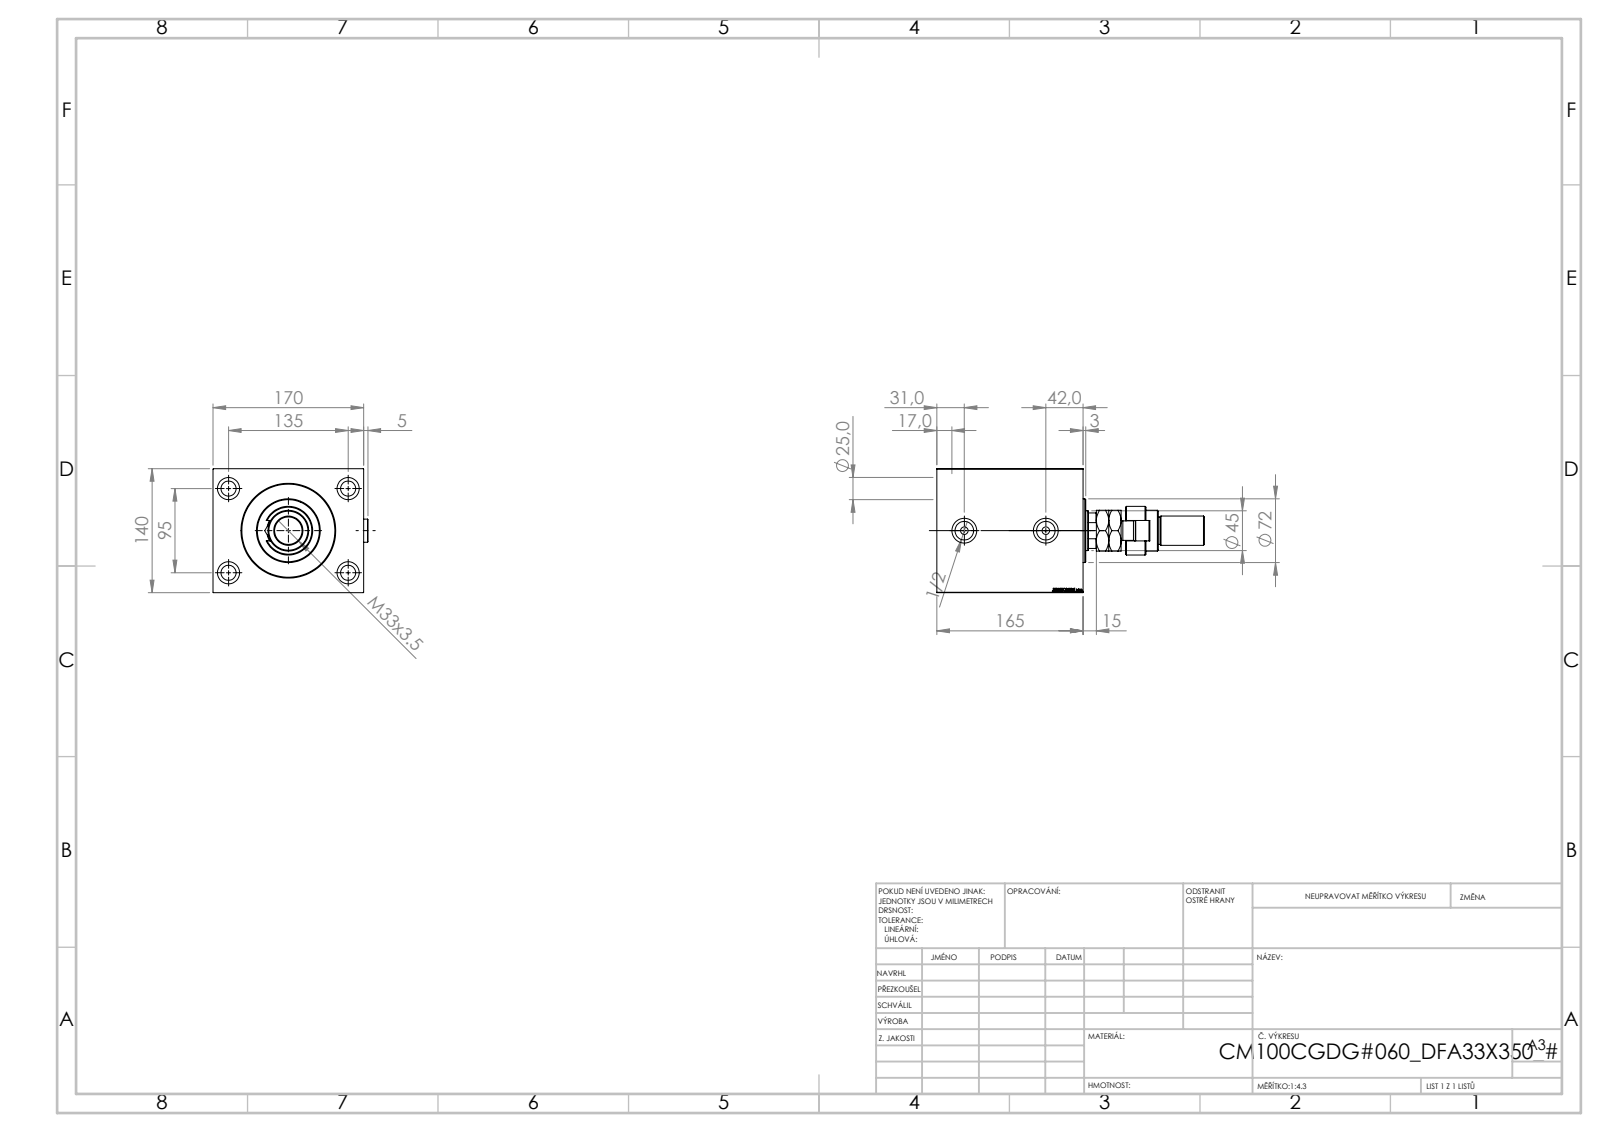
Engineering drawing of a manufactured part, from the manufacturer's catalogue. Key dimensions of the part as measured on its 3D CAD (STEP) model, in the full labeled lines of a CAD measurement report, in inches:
Part name (STEP PRODUCT): V450CM_VC_B; V450CM_C_Body; FEMALE_PART_FOR_DFA; V450CM_C_VCP (+2 more)
STEP written by: SolidWorks 2019 (CONFIG_CONTROL_DESIGN)
Units: inches
Bodies: 7 solids, 1004 faces (471 planar, 91 cylindrical, 442 other)
Overall size (bounding box): 11.89 × 6.886 × 5.512
Volume: 214 in³ · Surface area: 533 in²
Round holes (diameter × count): ⌀0.669 ×4, ⌀0.984 ×4, ⌀0.335 ×2, ⌀0.825 ×2, ⌀1.102 ×2, ⌀1.24 ×1, ⌀1.535 ×1, ⌀1.772 ×1, ⌀1.909 ×1, ⌀3.937 ×1, ⌀4.016 ×1, ⌀4.134 ×1
Round bosses / shafts (diameter × count): ⌀1.024 ×2, ⌀2.835 ×1, ⌀2.165 ×1, ⌀1.811 ×1, ⌀1.378 ×1, ⌀1.299 ×1, ⌀1.22 ×1, ⌀0.866 ×1
Partial cylindrical surfaces — rounded edges, fillets, slot ends (radius × count): R0.453 ×1, R0.866 ×1
Main face-to-face distances: 5.512, 6.693, 6.496, 1.024, 5.472, 3.543, 0.591, 2.362, 5.906, 2.953
Hole centre spacings: 3.25, 3.74, 5.315, 6.499, 3.622
